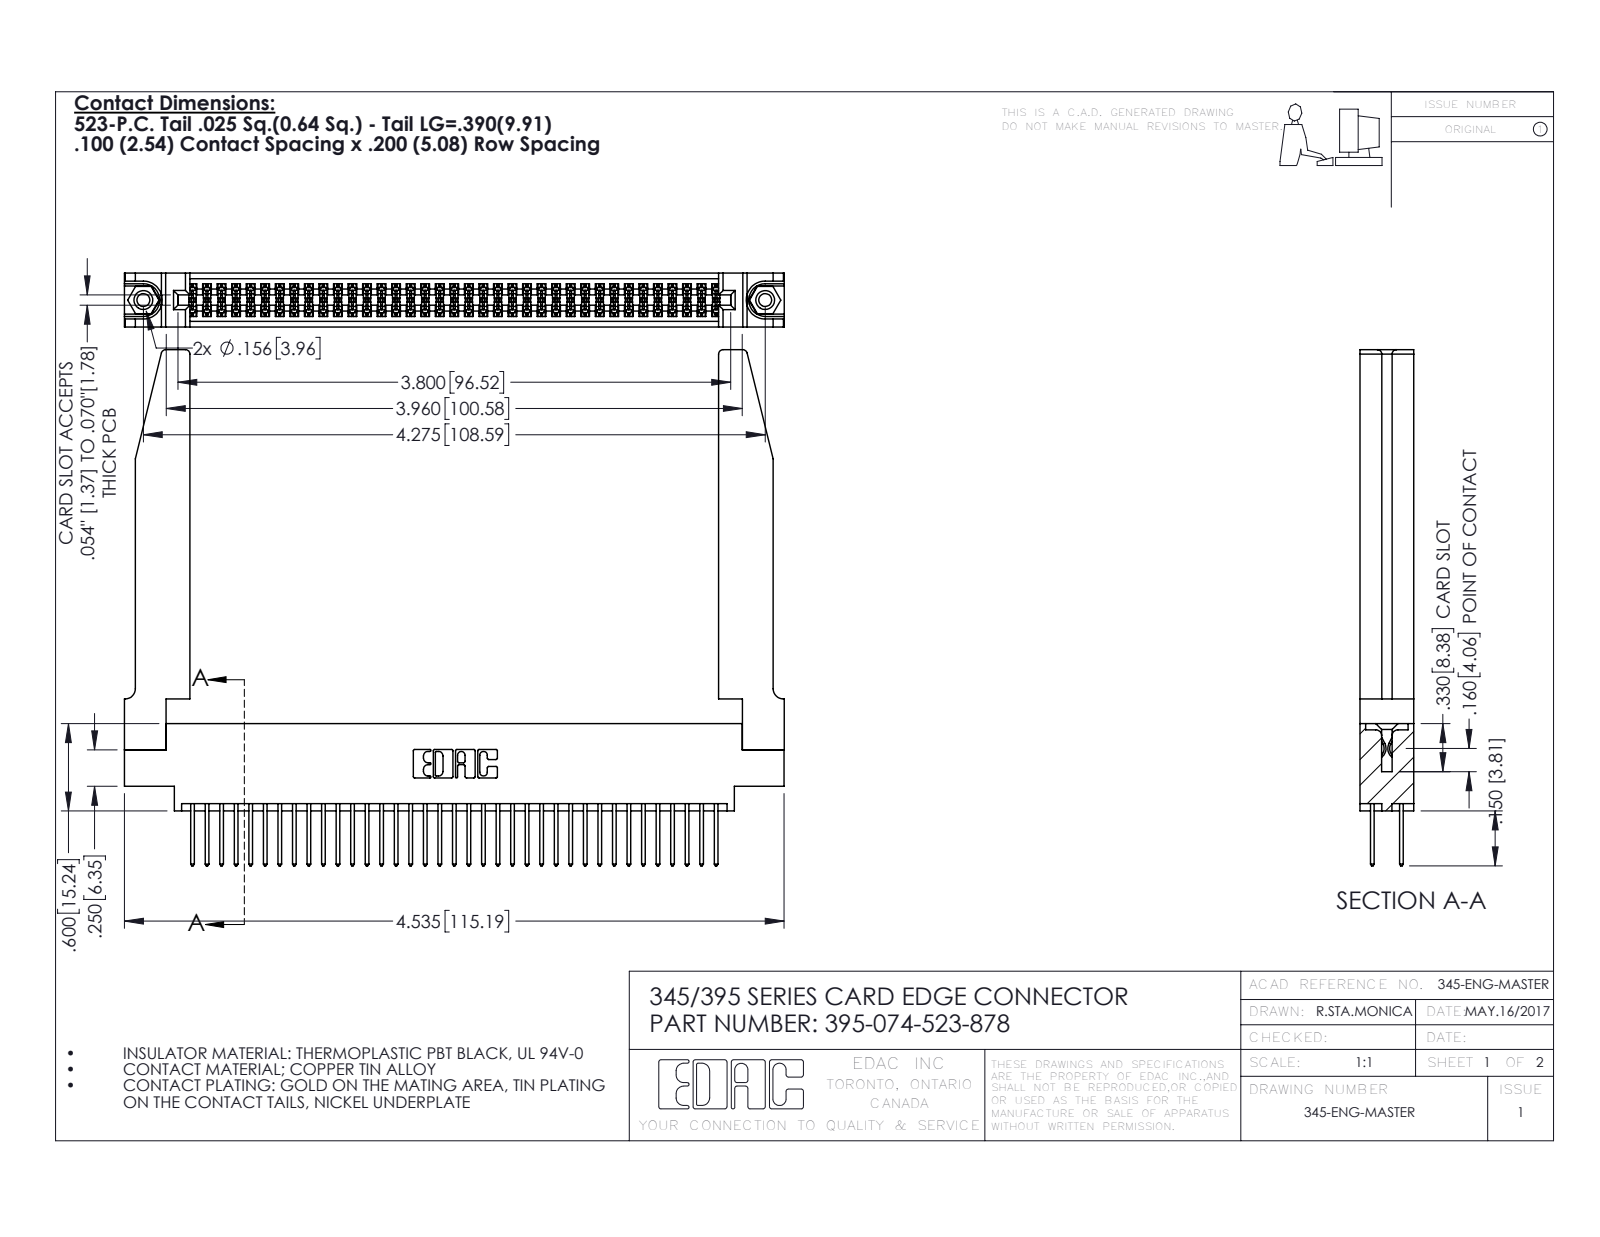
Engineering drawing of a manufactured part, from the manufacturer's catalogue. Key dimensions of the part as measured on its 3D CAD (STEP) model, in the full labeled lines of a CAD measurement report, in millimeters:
Part name (STEP PRODUCT): 395-074-523-878; 345-220-078_345-220-078; 345 Part_0.170 Offset - 0.156 Dia-TH; 345-250-001_345-250-001-102 (+1 more)
STEP written by: SolidWorks 2016 (CONFIG_CONTROL_DESIGN)
Units: millimetres
Bodies: 79 solids, 4064 faces (2668 planar, 1344 cylindrical, 52 other)
Overall size (bounding box): 115.2 × 90.1 × 9.4
Volume: 18 960 mm³ · Surface area: 24 100 mm²
Round holes (diameter × count): ⌀2.3 ×2, ⌀3.2 ×2, ⌀4 ×2, ⌀1.6 ×1
Round bosses / shafts (diameter × count): ⌀3.9 ×2
Partial cylindrical surfaces — rounded edges, fillets, slot ends (radius × count): R0.2 ×111, R0.3 ×74, R0.3 ×22, R0.8 ×8, R0.2 ×6, R0.8 ×6, R0.7 ×3, R0.4 ×2
Main face-to-face distances: 1.8, 9.4, 7.6, 2.5, 6.9, 0.6, 5.1, 5.7, 4.4, 3.8
Hole centre spacings: 6.9, 102.6, 108.6
